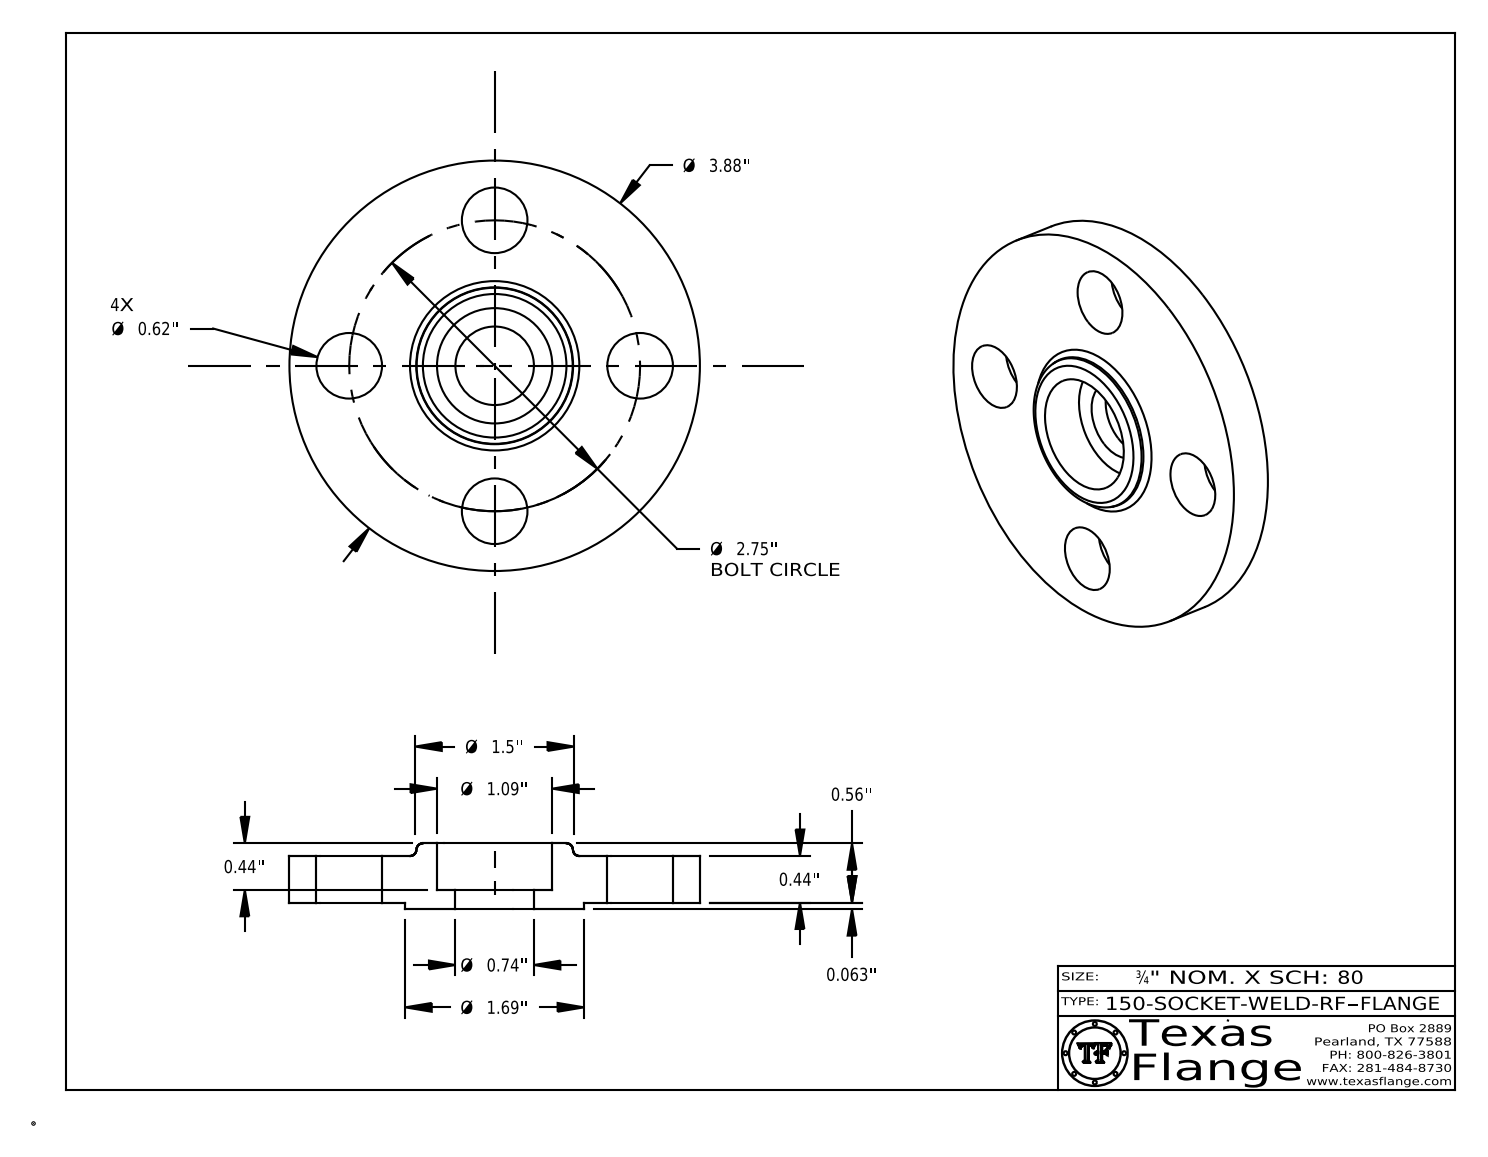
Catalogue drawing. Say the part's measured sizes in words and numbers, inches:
The part is named "150-SOCKET-WELD-RF". Its 3-D file was written by "CATIA V5 STEP AP214 (AUTOMOTIVE_DESIGN)". It is 1 solid with 412 faces: 370 planar, 36 cylindrical and 6 other. Overall it measures 3.88 by 3.88 by 0.623 inches. Its volume is 4.527 cubic inches and its surface area 31.83 square inches. Round holes: 4 of diameter 0.62, 1 of diameter 0.495, 1 of diameter 0.742, 1 of diameter 1.09. Round bosses or shafts: 8 of diameter 0.03, 1 of diameter 3.88, 1 of diameter 1.69, 1 of diameter 0.39. The main face-to-face distances are 0.44, 0.063, 0.503, 0.622, 0.56, 0.12, 0.183, 0.12, 0.32, 0.44. The hole center spacings are 1.375, 1.945, 1.052, 2.541, 2.75.
